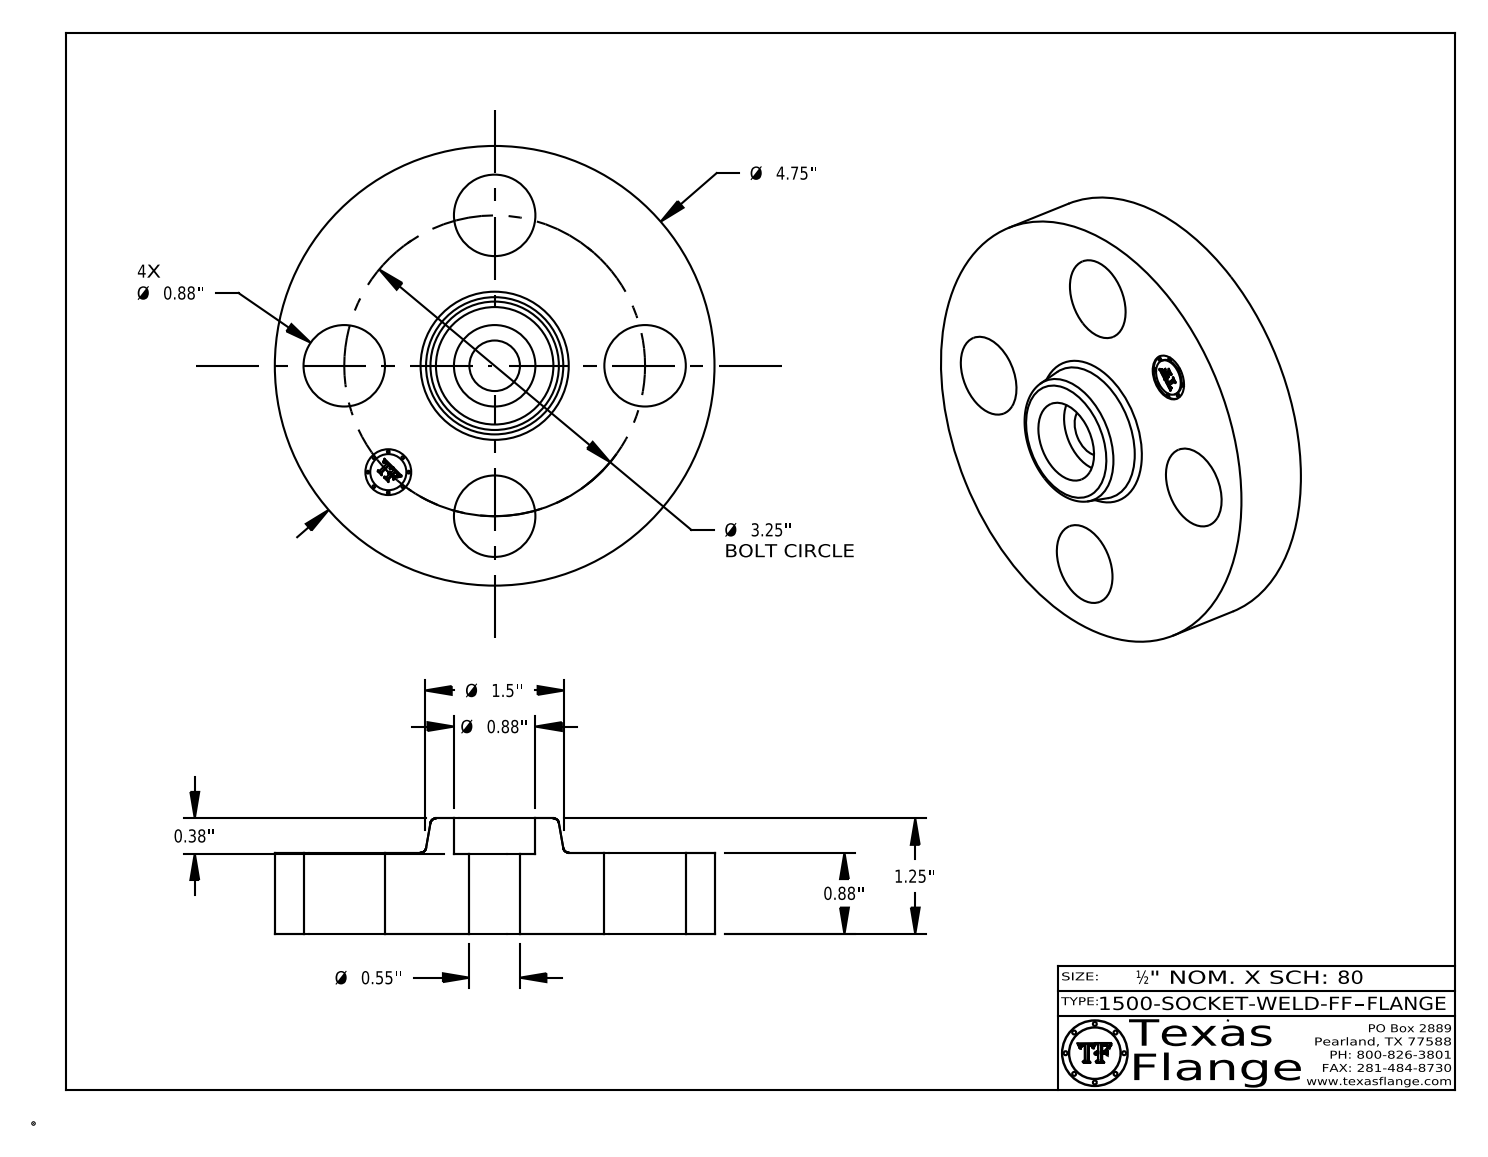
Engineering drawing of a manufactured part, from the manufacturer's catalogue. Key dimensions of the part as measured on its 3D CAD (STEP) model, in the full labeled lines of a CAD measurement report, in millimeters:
Part name (STEP PRODUCT): 1500-SOCKET-WELD-FF
STEP written by: CATIA V5 STEP AP214 (AUTOMOTIVE_DESIGN)
Units: millimetres
Bodies: 1 solid, 409 faces (369 planar, 34 cylindrical, 6 other)
Overall size (bounding box): 120.7 × 120.7 × 31.8
Volume: 223 200 mm³ · Surface area: 36 680 mm²
Round holes (diameter × count): ⌀22.4 ×5, ⌀12.6 ×1, ⌀13.9 ×1
Round bosses / shafts (diameter × count): ⌀0.8 ×8, ⌀120.7 ×1, ⌀9.9 ×1
Main face-to-face distances: 22.4, 31.8, 9.4, 22.1, 9.7, 22, 0.4, 9.8, 3.8, 3.7
Hole centre spacings: 41.3, 58.4, 31.6, 76.3, 82.6
